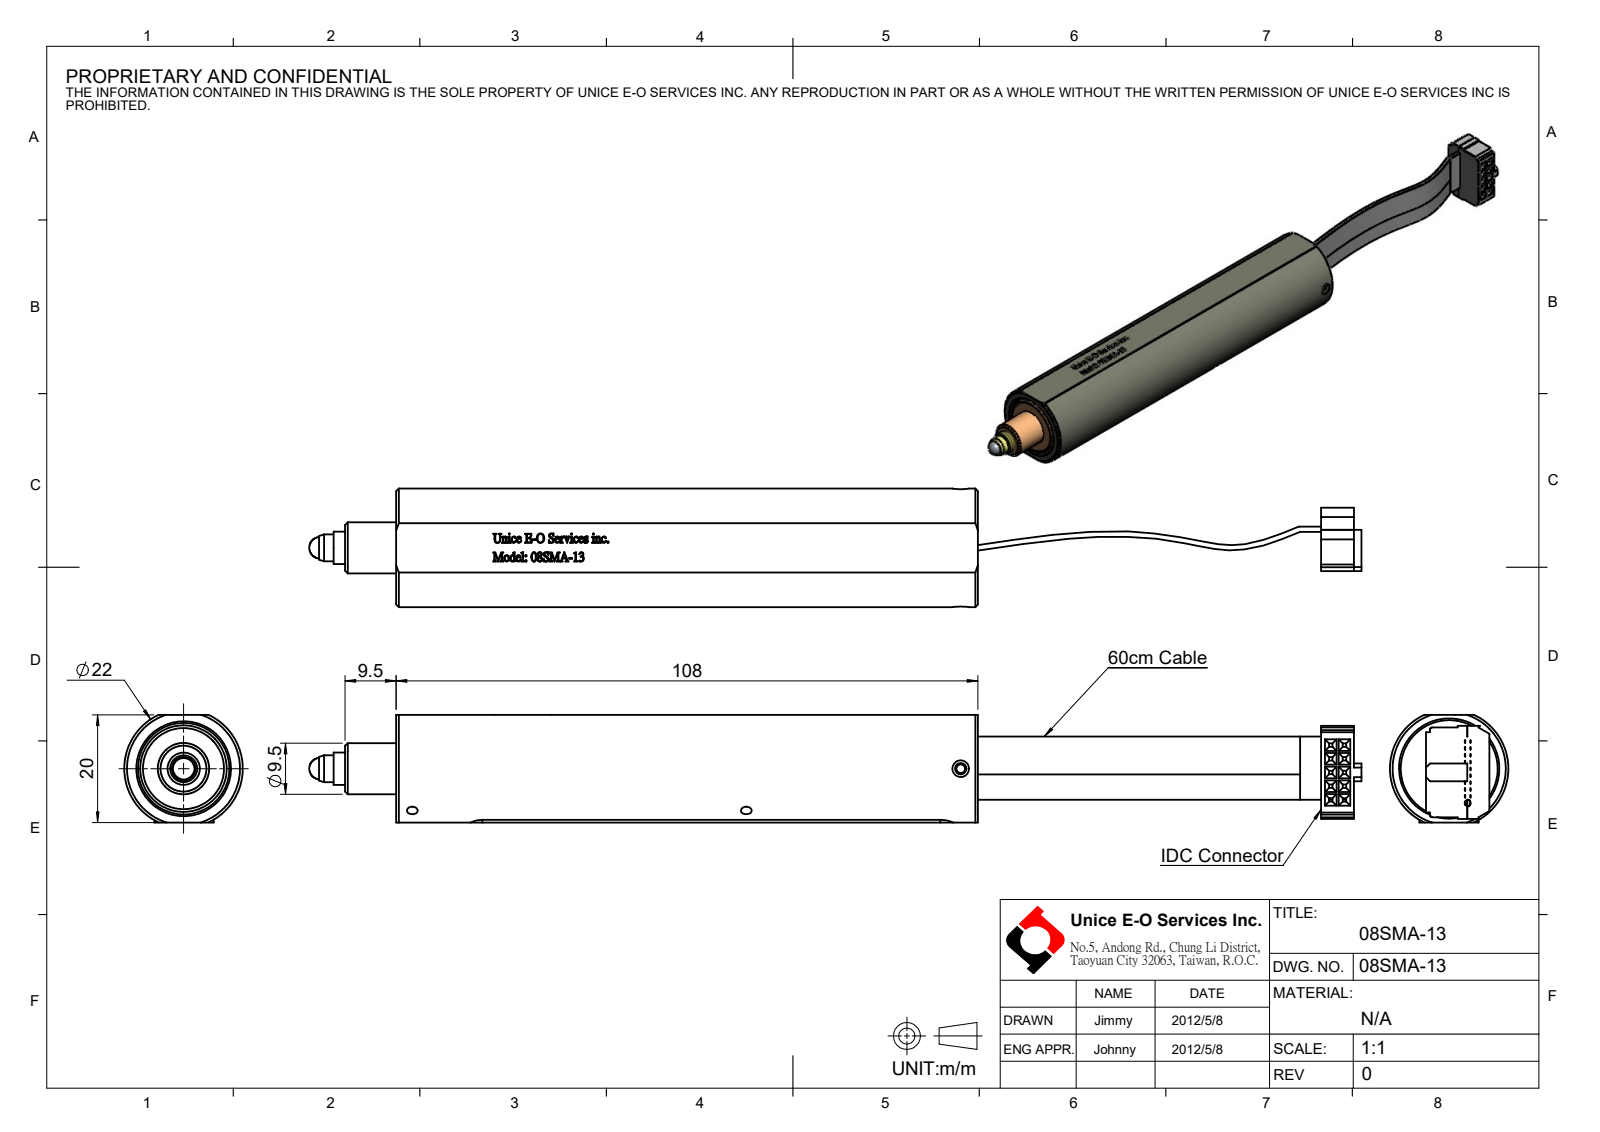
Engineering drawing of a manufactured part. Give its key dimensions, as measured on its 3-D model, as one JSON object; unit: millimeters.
{"part_name": "08SMA-13", "step_written_by": "SolidWorks 2016 (CONFIG_CONTROL_DESIGN)", "units": "millimeters", "bodies": {"solids": 20, "faces": 1503, "planar": 707, "cylindrical": 246, "other": 550}, "overall_size": [195.29, 22, 20], "volume_mm3": 30410, "surface_area_mm2": 28156, "round_holes": [[1.7, 5], [2, 5], [1.25, 4], [2.05, 4], [1.6, 3], [1.48, 2], [2.2, 2], [3, 2], [2.1, 1], [3.1, 1], [4, 1], [5.1, 1]], "round_bosses_or_shafts": [[1.8, 8], [16, 1], [15.5, 1], [15, 1], [14.8, 1], [12, 1], [9.5, 1], [9, 1]], "partial_cylinders_radius": [[0.48, 10], [0.64, 10], [3, 7], [0.5, 2], [0.51, 2], [0.61, 2], [0.75, 2], [1, 2]], "face_to_face_distances": [0.8, 20, 19.2, 2, 1.65, 18.4, 0.85, 18.35, 1, 23.1], "hole_center_spacings": [87, 87.28, 7, 7.78, 0.48, 5.46, 5.51, 6.95]}
